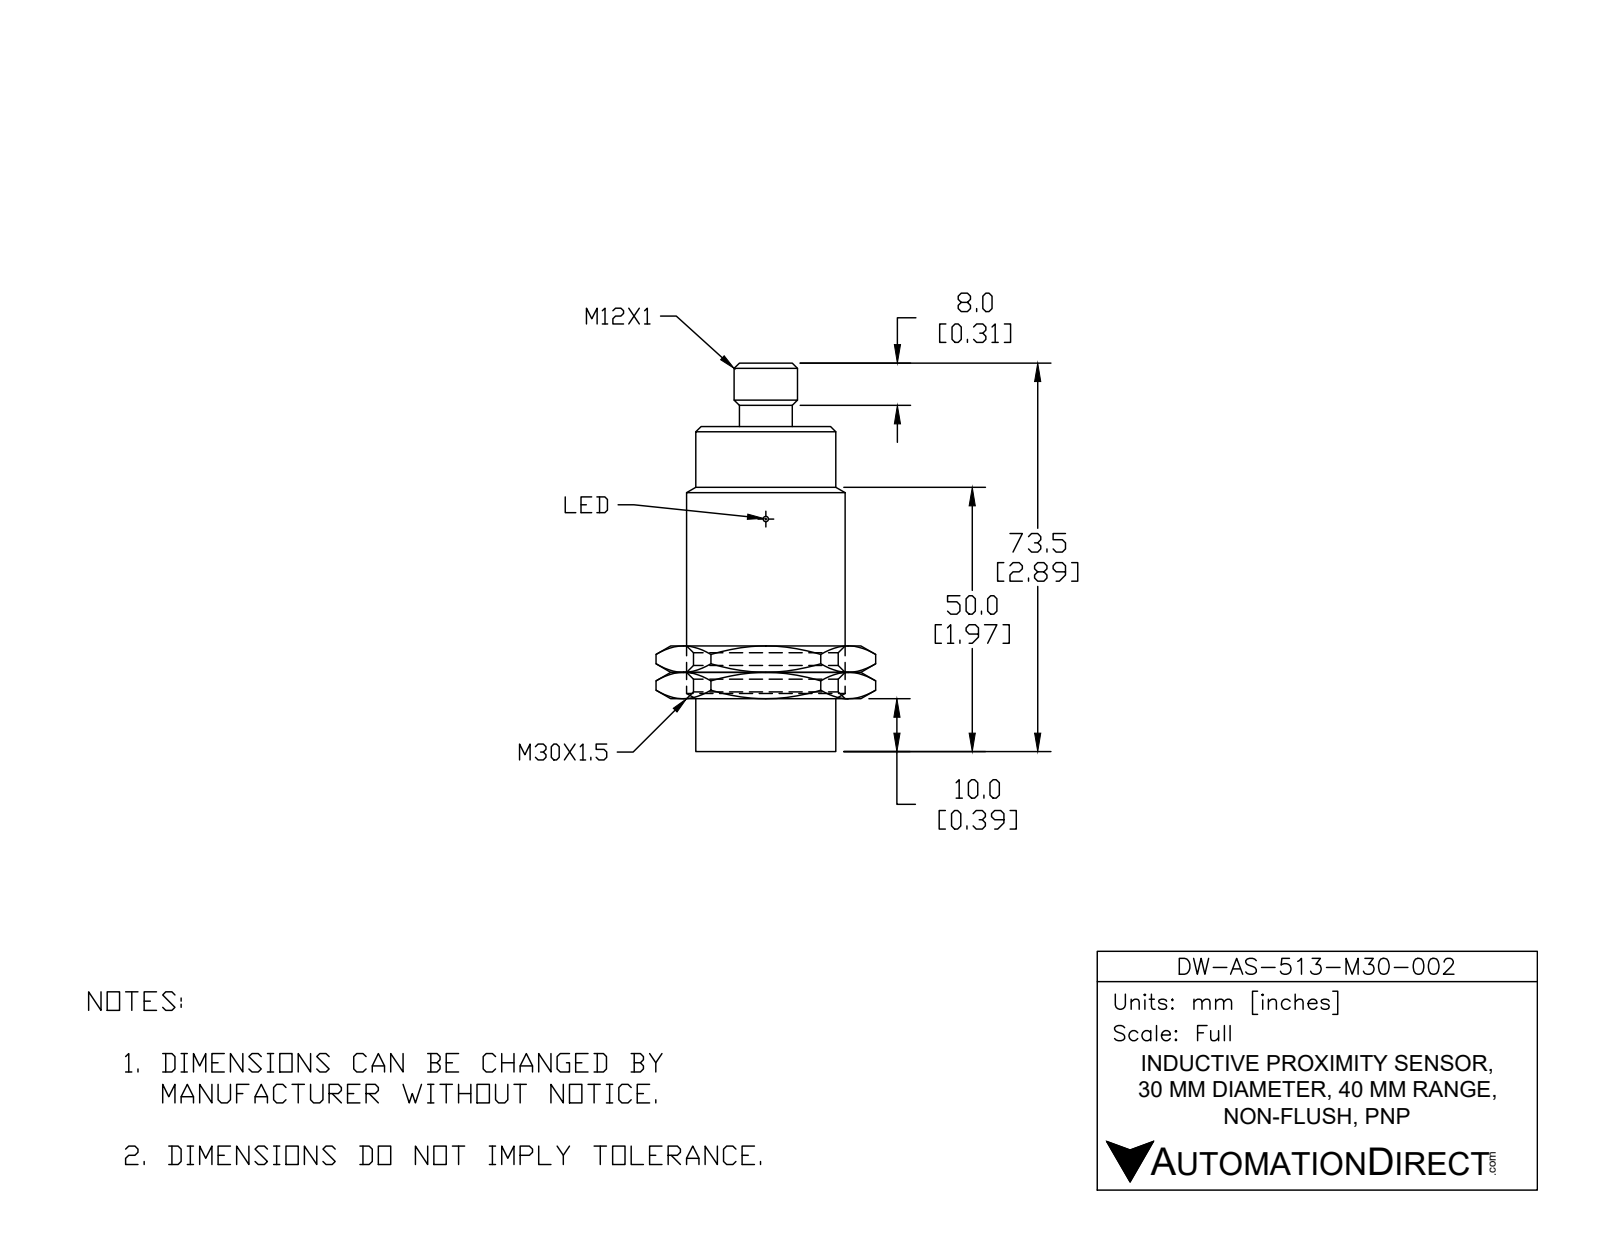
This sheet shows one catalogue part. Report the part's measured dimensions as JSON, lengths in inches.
{"part_name": "DW-AS-513-M30-002", "step_written_by": "SolidWorks 2017 (AUTOMOTIVE_DESIGN)", "units": "inches", "bodies": {"solids": 1, "faces": 36, "planar": 13, "cylindrical": 14, "other": 9}, "overall_size": [2.896, 1.181, 1.181], "volume_in3": 2.531, "surface_area_in2": 12.1, "round_holes": [[0.12, 2], [0.335, 1]], "round_bosses_or_shafts": [[0.043, 3], [1.181, 1], [1.095, 1], [1.083, 1], [0.472, 1], [0.415, 1]], "partial_cylinders_radius": [[0.019, 2], [0.022, 1]], "face_to_face_distances": [2.382, 2.553, 0.171, 2.047, 0.335, 0.506, 0.394, 1.654, 1.988, 2.159]}
